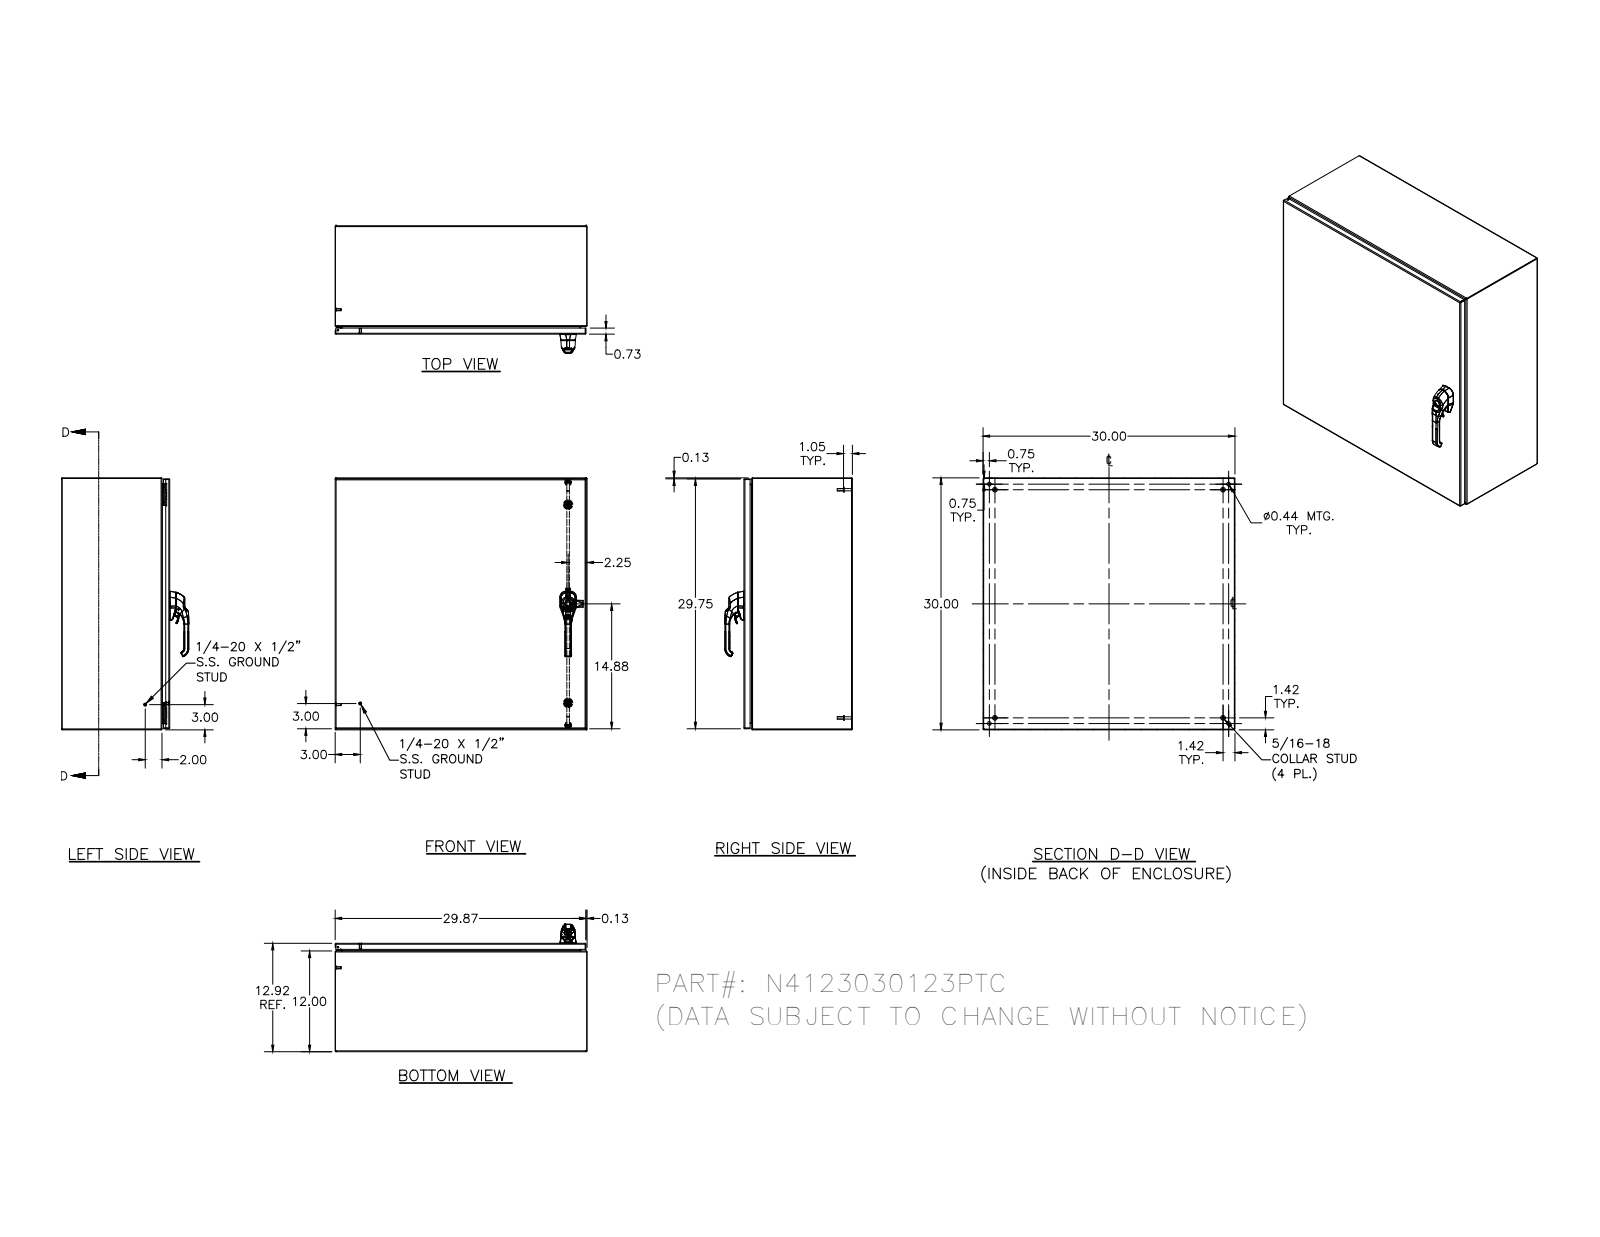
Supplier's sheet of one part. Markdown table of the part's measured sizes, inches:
| quantity | value |
| --- | --- |
| part name | N4123030123PTC; N4123030123PTCBKP; N41230303PTCLID; HFW328176 (+8 more) |
| STEP written by | Autodesk Inventor 2011 (AUTOMOTIVE_DESIGN) |
| units | inches |
| bodies | 49 solids, 2962 faces (941 planar, 1101 cylindrical, 920 other) |
| overall size | 30 × 30 × 15.186 |
| volume | 260.4 in³ |
| surface area | 7 120 in² |
| round holes (diameter × count) | 0.188 × 5, 0.093 × 4, 0.152 × 4, 0.165 × 4, 0.167 × 4, 0.172 × 4, 0.197 × 4, 0.437 × 4, 0.213 × 3, 0.236 × 3, 0.354 × 3, 0.106 × 2 |
| round bosses / shafts (diameter × count) | 0.25 × 10, 0.563 × 4, 0.36 × 4, 0.32 × 4, 0.3 × 4, 0.275 × 4, 0.256 × 4, 0.236 × 4 |
| partial cylindrical surfaces (radius × count) | 0.02 × 195, 0.012 × 78, 0.118 × 33, 0.031 × 30, 0.05 × 26, 0.019 × 22, 0.105 × 20, 0.016 × 18 |
| main face-to-face distances | 0.074, 12.843, 29.926, 12.917, 12.769, 29.852, 30, 11.926, 0.917, 0.739 |
| hole center spacings | 25.996, 27.393, 28.5, 0.017, 0.66, 26.656, 0.019, 0.177 |
